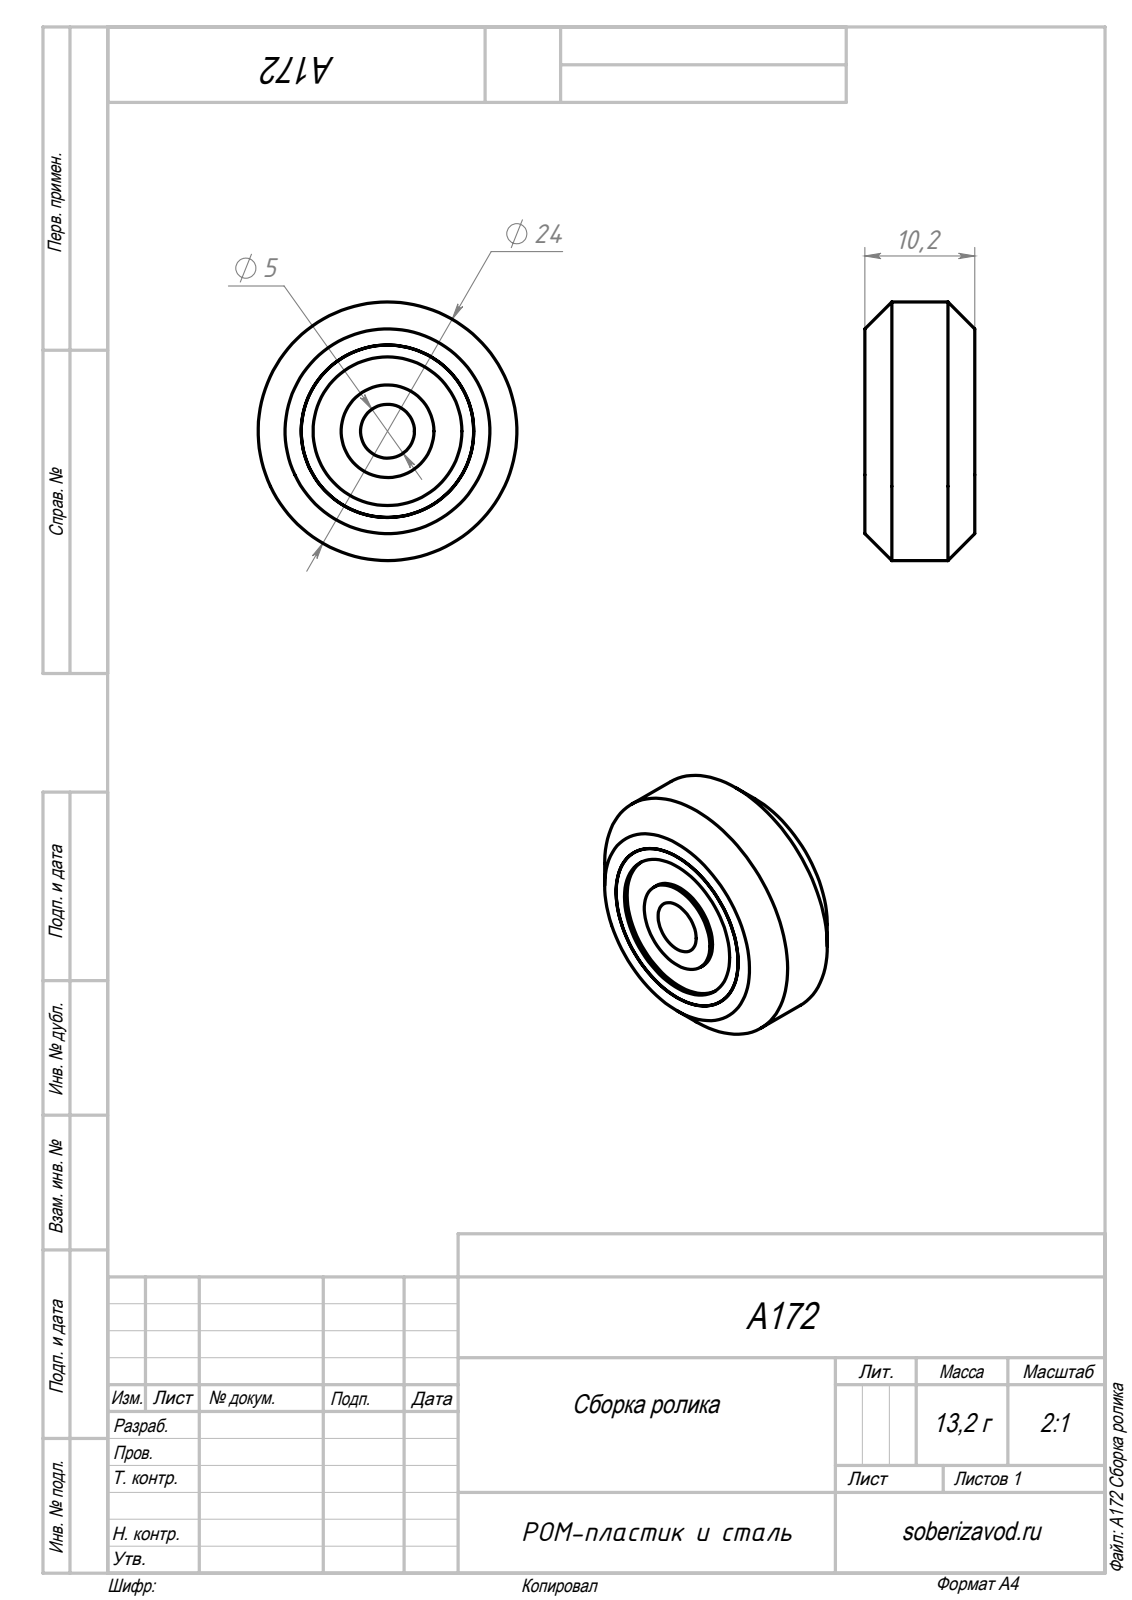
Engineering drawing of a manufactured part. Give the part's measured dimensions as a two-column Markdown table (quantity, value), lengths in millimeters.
| quantity | value |
| --- | --- |
| part name | A211 Высокоточная дистанционная шайба 5 мм_00; A172 Сборка ролика; A180 Подшипник 625rs, O 5 O 16 |
| STEP written by | SolidWorks 2018 (AUTOMOTIVE_DESIGN) |
| units | millimeters |
| bodies | 4 solids, 58 faces (18 planar, 36 cylindrical, 4 other) |
| overall size | 24 × 24 × 10.2 |
| volume | 3 906 mm³ |
| surface area | 3 283 mm² |
| round holes (diameter × count) | 5 × 1, 5.2 × 1, 13.8 × 1, 14 × 1, 16 × 1 |
| round bosses / shafts (diameter × count) | 24 × 1, 10 × 1, 8.6 × 1 |
| main face-to-face distances | 0.35, 4.65, 5.2, 0.9, 5.55, 9.85, 4.3, 5, 4.85, 0.55 |
